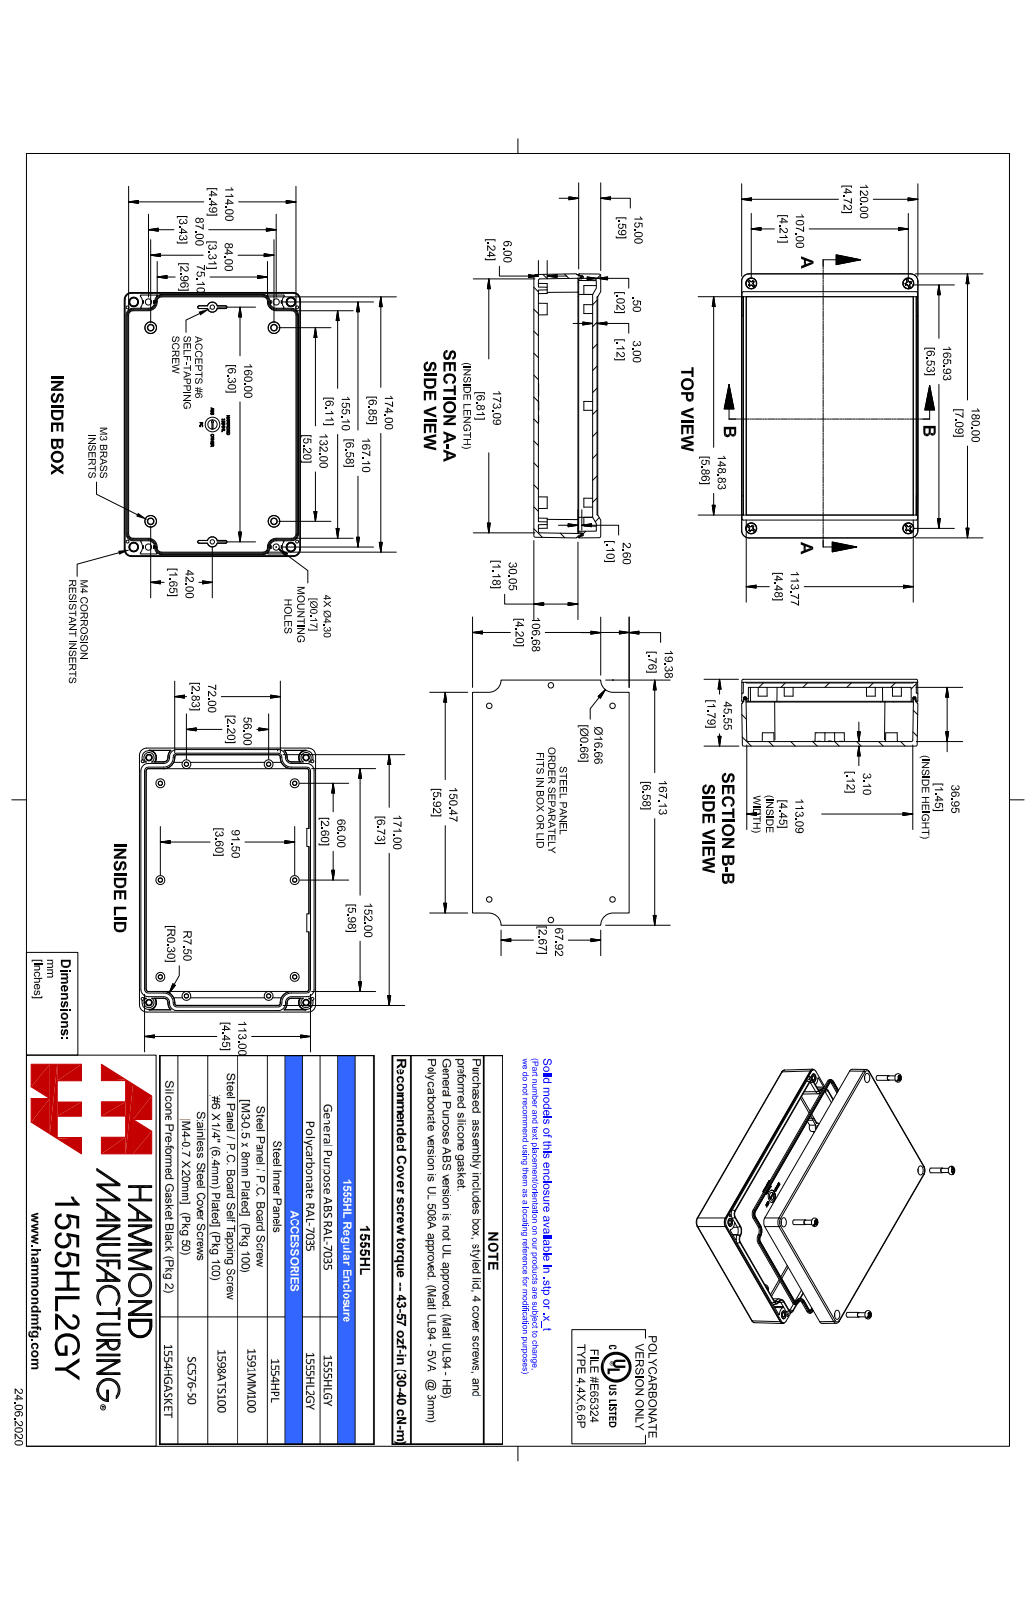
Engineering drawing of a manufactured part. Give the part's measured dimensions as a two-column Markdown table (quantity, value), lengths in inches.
| quantity | value |
| --- | --- |
| part name | 1555HL2GY |
| STEP written by | SolidWorks 2021 (AUTOMOTIVE_DESIGN) |
| units | inches |
| bodies | 15 solids, 1504 faces (412 planar, 328 cylindrical, 764 other) |
| overall size | 7.089 × 4.727 × 1.793 |
| volume | 13.29 in³ |
| surface area | 244 in² |
| round holes (diameter × count) | 0.079 × 4, 0.097 × 4, 0.128 × 4, 0.138 × 4, 0.181 × 4, 0.276 × 4 |
| round bosses / shafts (diameter × count) | 0.25 × 4, 0.236 × 4, 0.218 × 4, 0.21 × 4, 0.19 × 4, 0.154 × 4, 0.153 × 4, 0.15 × 4 |
| partial cylindrical surfaces (radius × count) | 0.02 × 24, 0.039 × 18, 0.197 × 8, 0.031 × 4, 0.118 × 4, 0.187 × 4 |
| main face-to-face distances | 0.118, 0.122, 1.695, 1.573, 1.577, 1.455, 0.12, 0.177, 0.138, 0.098 |
| hole center spacings | 0.196, 0.197, 0.824, 0.827, 0.859, 3.822, 3.825, 3.974 |
